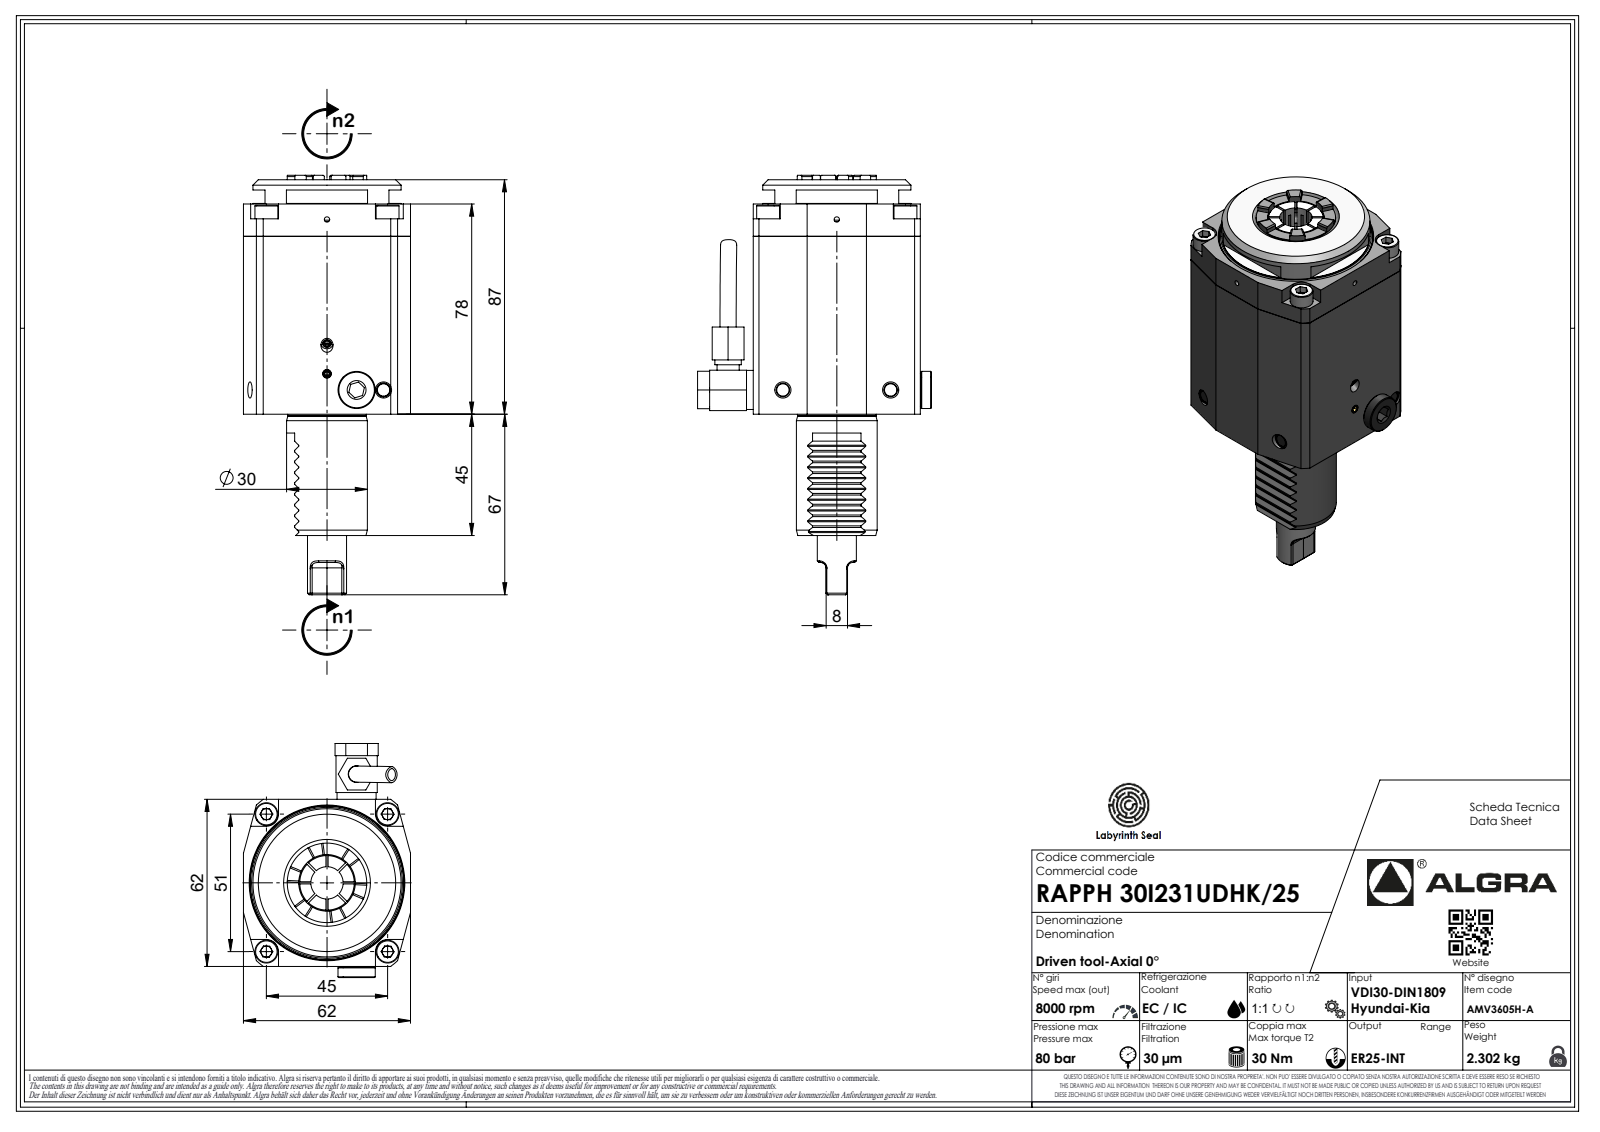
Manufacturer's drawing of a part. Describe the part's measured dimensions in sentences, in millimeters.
The part is named "RAPPH30I231UDHK25". Its 3-D file was written by "SolidWorks 2023 (AUTOMOTIVE_DESIGN)". It is 1 solid with 543 faces: 340 planar, 80 cylindrical and 123 other. Overall it measures 155.65 by 86.85 by 62 millimeters. Its volume is 341 902 cubic millimeters and its surface area 35 265 square millimeters. Round holes: 1 of diameter 2.1. Round bosses or shafts: 2 of diameter 14.5, 1 of diameter 55, 1 of diameter 30, 1 of diameter 29.1, 1 of diameter 13.8, 1 of diameter 12, 1 of diameter 9.8, 1 of diameter 8.2. Partial cylindrical surfaces (rounded edges, fillets, slot ends): 10 of radius 35, 9 of radius 0.3, 7 of radius 0.33, 7 of radius 0.52, 7 of radius 3.7, 6 of radius 2, 1 of radius 0.21, 1 of radius 7.65. The main face-to-face distances are 62, 65.58, 87, 78, 9, 8, 54, 2.83, 45, 123.
